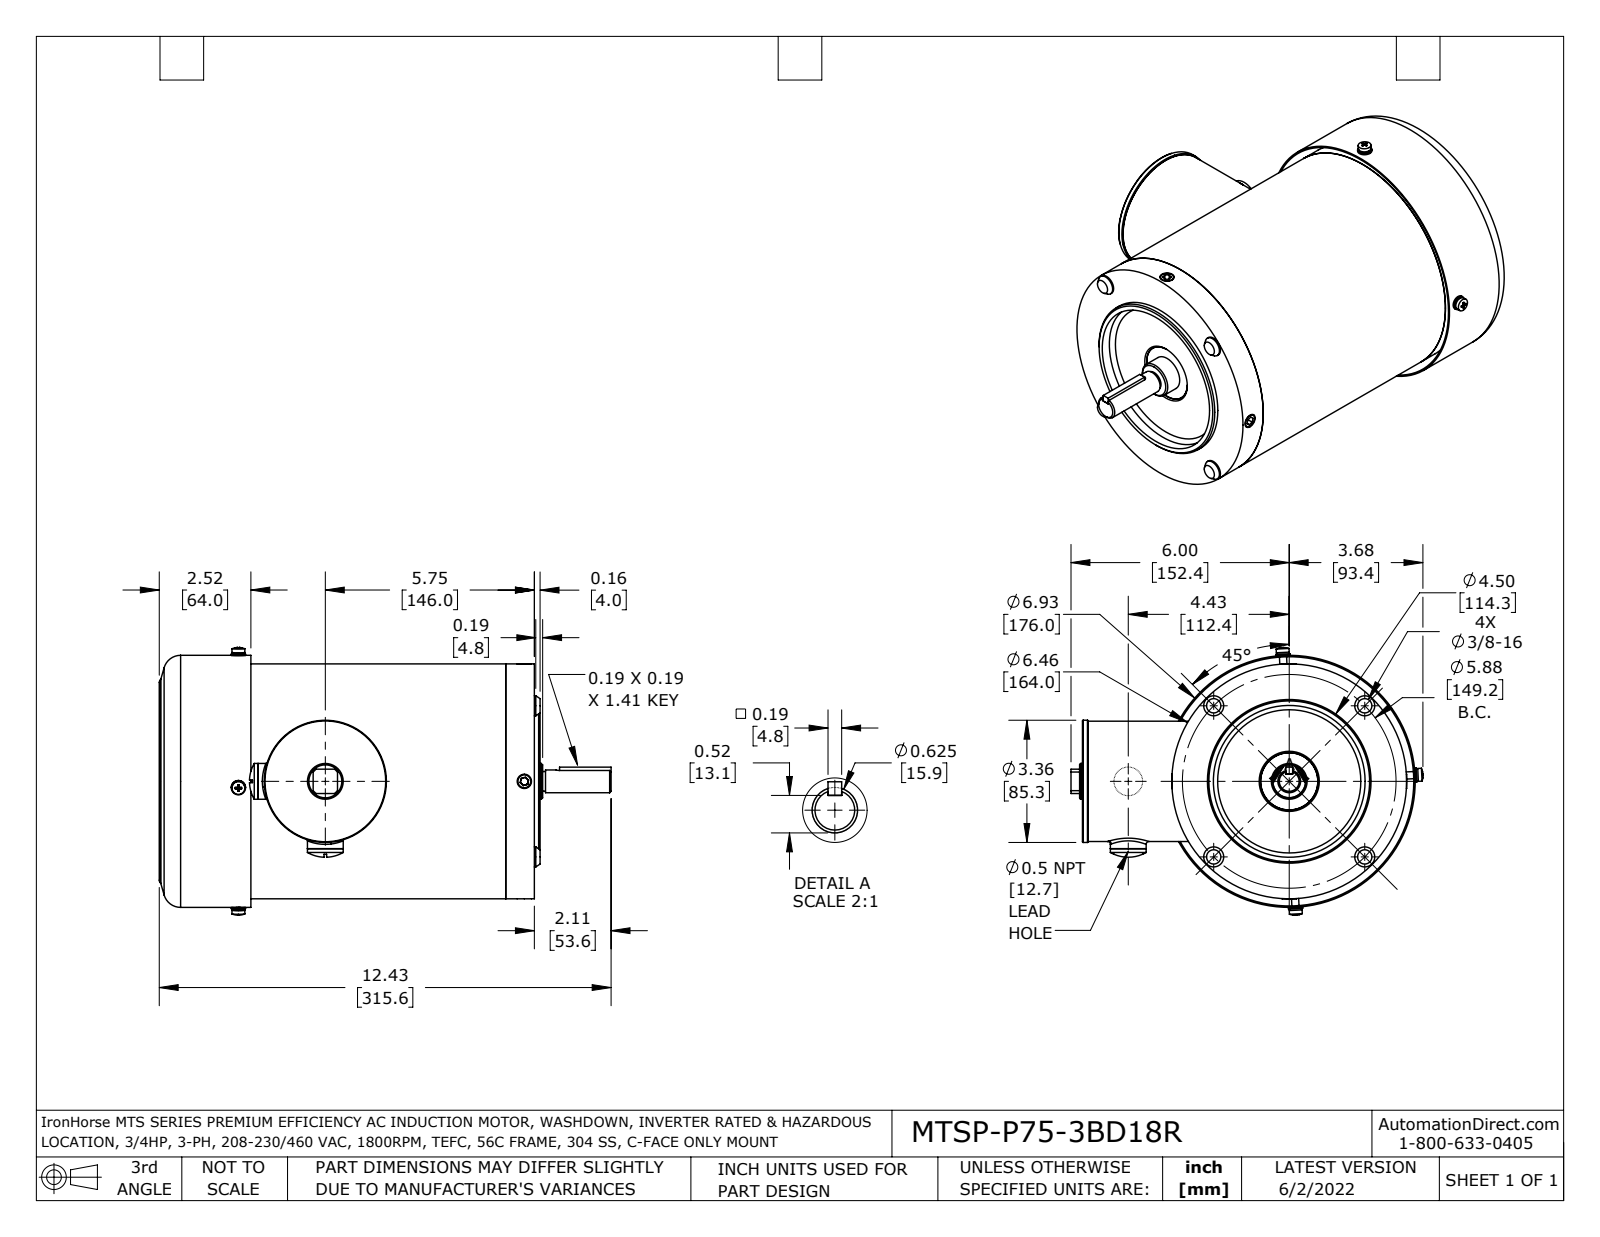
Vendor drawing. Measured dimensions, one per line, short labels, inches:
name: MTSP-P75-3BD18R
written by: SolidWorks 2021 (AUTOMOTIVE_DESIGN)
unit: in
bodies: 39 solids, 1359 faces (386 planar, 483 cylindrical, 490 other)
size: 12.425 × 9.68 × 7.357
volume: 52.54 in³; area: 900.2 in²
holes: 10× ⌀0.165, 8× ⌀0.217, 4× ⌀0.213, 4× ⌀0.236, 4× ⌀0.335, 2× ⌀0.118, 2× ⌀0.354, 2× ⌀0.472, 2× ⌀0.656, 2× ⌀1.378, 1× ⌀0.984, 1× ⌀1.024
bosses: 6× ⌀0.394, 4× ⌀0.551, 4× ⌀0.354, 4× ⌀0.331, 4× ⌀0.315, 4× ⌀0.197, 3× ⌀0.984, 2× ⌀0.787
rounds: 36× R0.128, 35× R0.039, 32× R0.079, 16× R0.012, 9× R0.118, 8× R0.236, 4× R0.217, 4× R0.394
face distances: 0.118, 8.307, 0.236, 0.039, 8.071, 8.189, 8.425, 1.949, 1.831, 10.256
hole spacings: 2.937, 4.154, 0.143, 1.181, 1.322, 2.231, 2.311, 2.498
